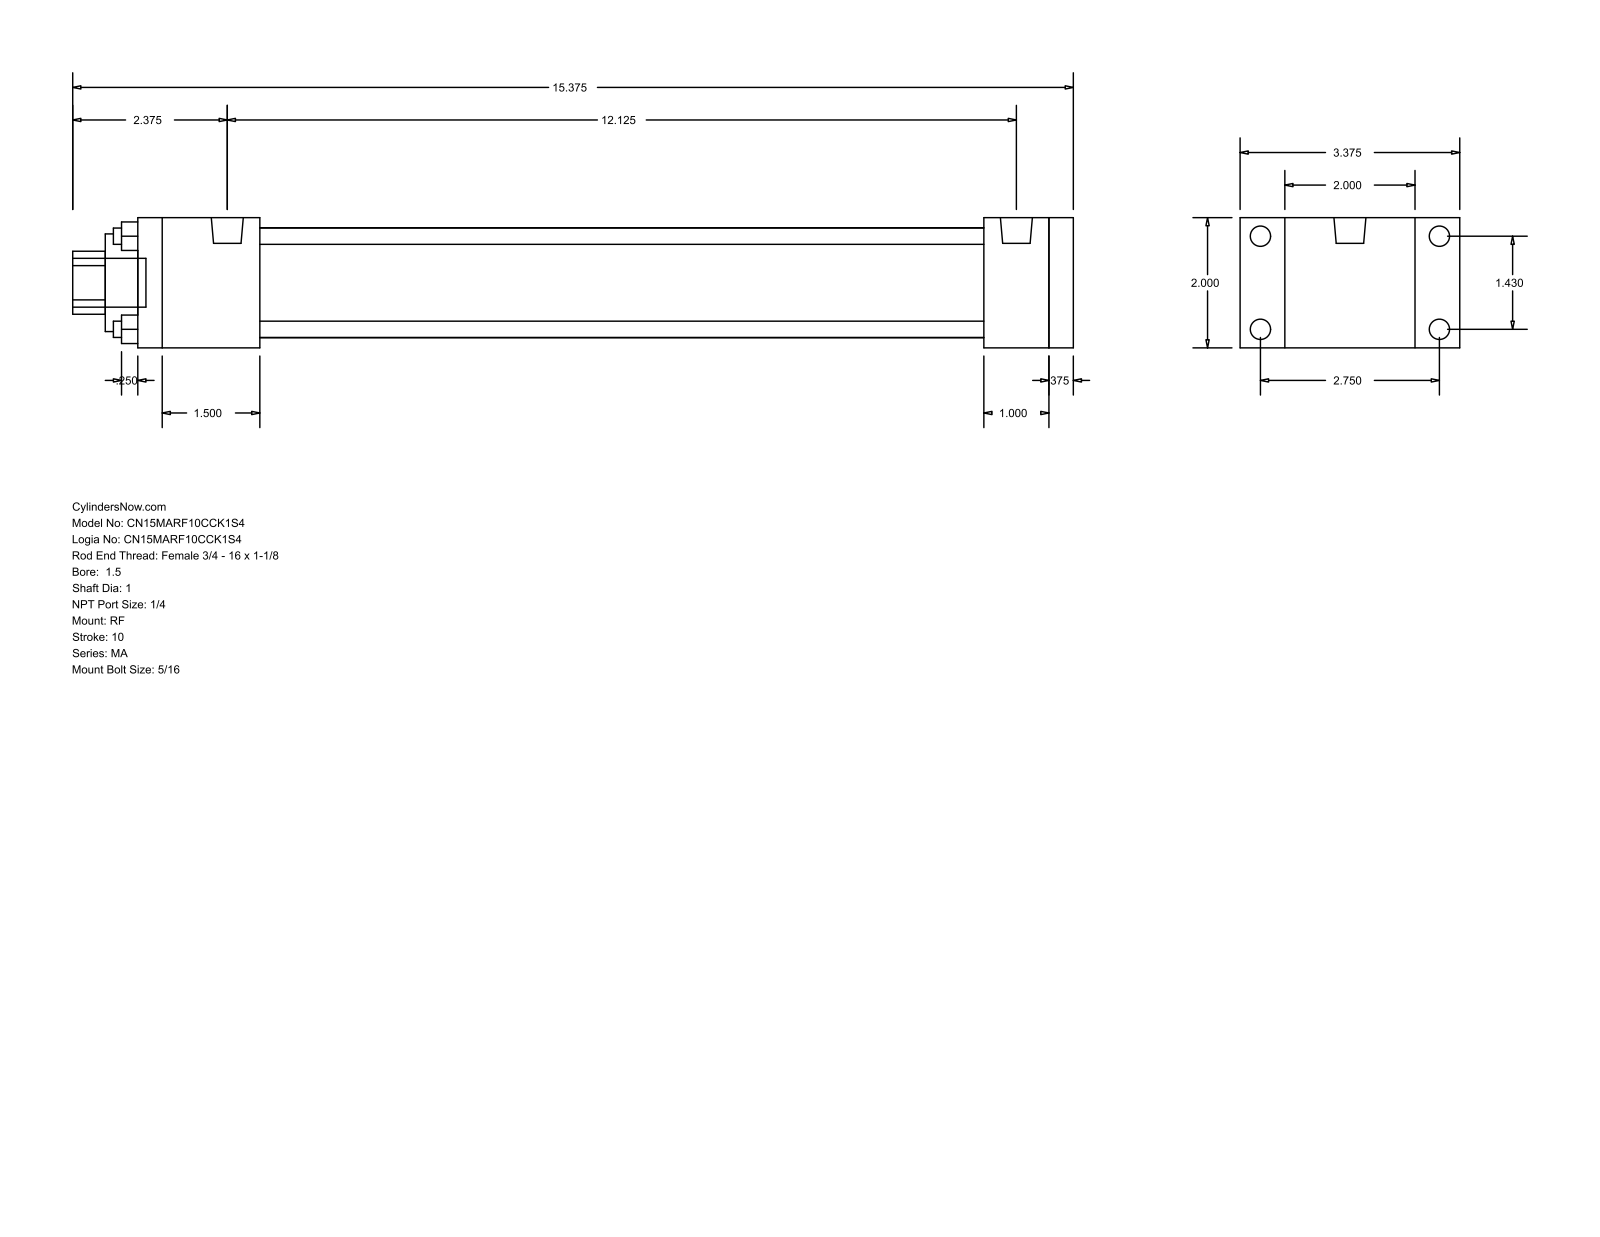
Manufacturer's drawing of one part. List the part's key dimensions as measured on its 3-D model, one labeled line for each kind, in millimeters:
Part name (STEP PRODUCT): MA_RF__0150_1
STEP written by: GSSL Pune (CONFIG_CONTROL_DESIGN)
Units: millimetres
Bodies: 0 solids, 92 faces (64 planar, 28 cylindrical, 0 other)
Overall size (bounding box): 390.52 × 85.72 × 50.8
Round holes (diameter × count): ⌀6.35 ×4, ⌀25.4 ×1, ⌀38.1 ×1, ⌀42.93 ×1
Round bosses / shafts (diameter × count): ⌀7.94 ×8, ⌀12.49 ×2, ⌀19.05 ×1
Partial cylindrical surfaces — rounded edges, fillets, slot ends (radius × count): R12.29 ×1
Main face-to-face distances: 50.8, 9.52, 365.12, 355.6, 25.4, 330.2, 34.92, 47.63, 282.57, 307.97
Hole centre spacings: 25.68, 36.32, 51.36
